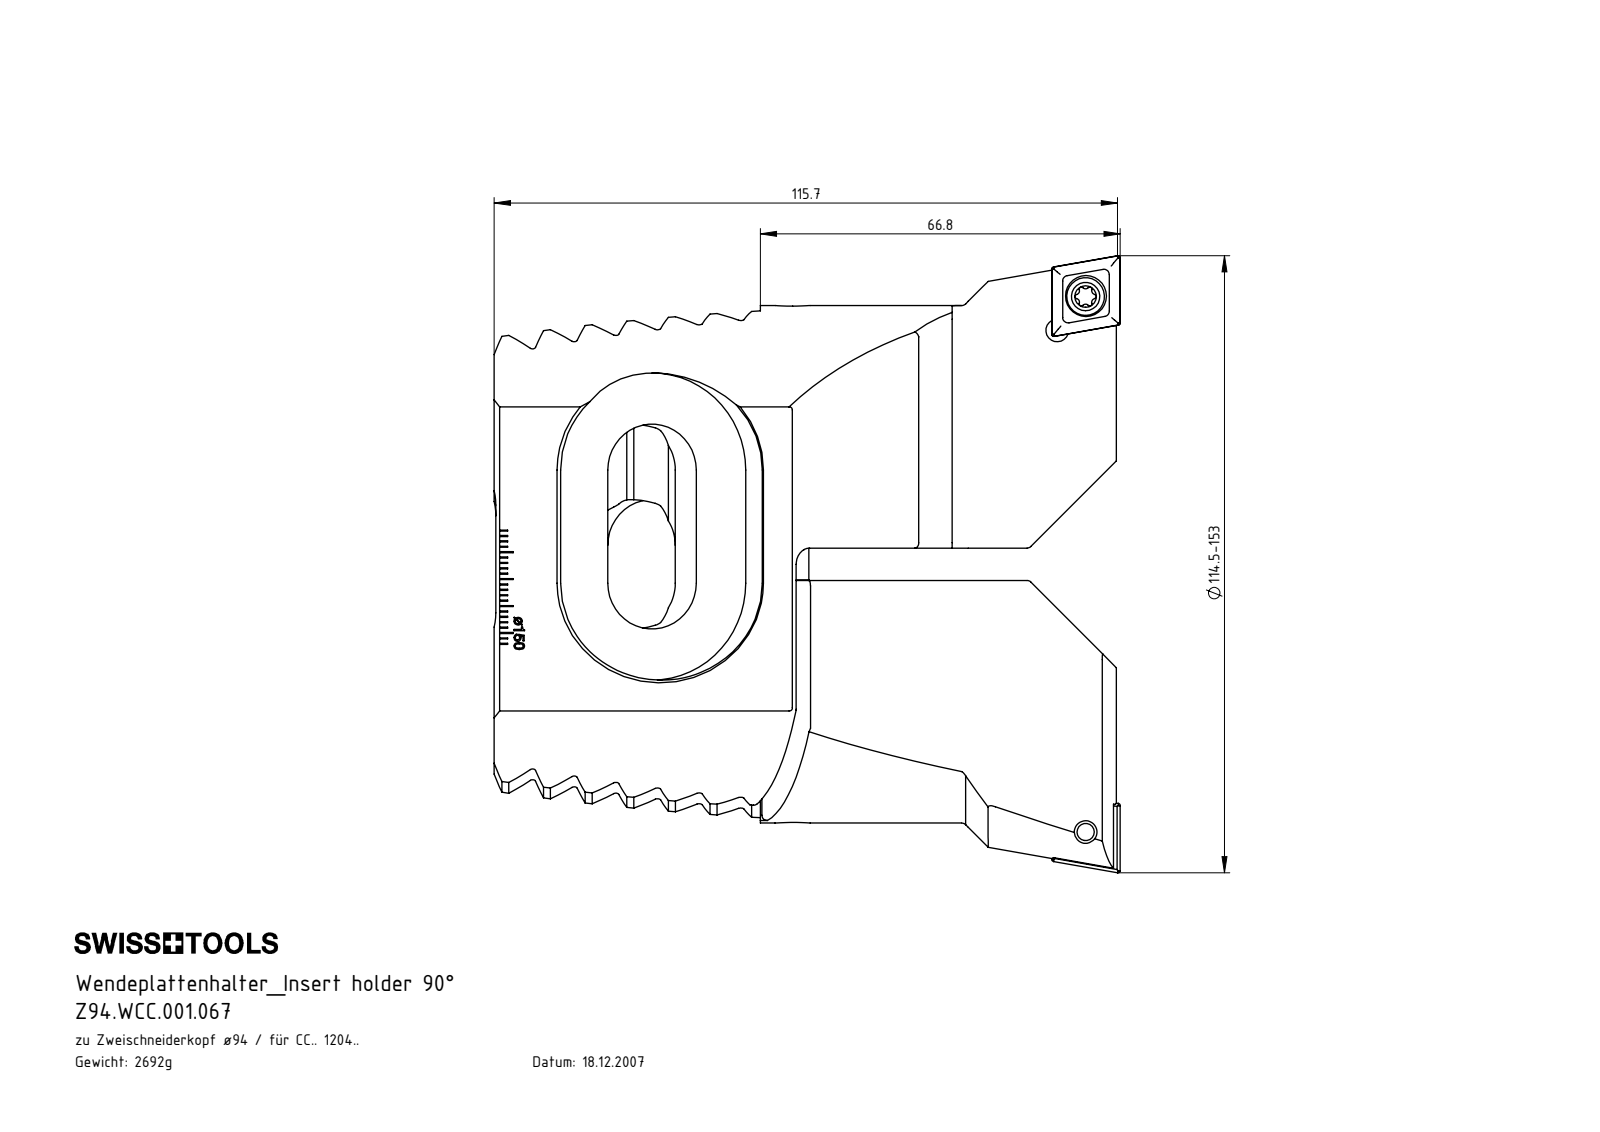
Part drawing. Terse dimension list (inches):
name: CCMT120404; Z94.WCC.001.067; WCC-ER2.001.010_A; Z94-xxx.001.067_E (+1 more)
written by: SolidWorks 2017 (AUTOMOTIVE_DESIGN)
unit: in
bodies: 8 solids, 782 faces (444 planar, 134 cylindrical, 204 other)
size: 4.575 × 4.508 × 2.961
volume: 20.93 in³; area: 99.83 in²
holes: 4× ⌀0.165, 2× ⌀0.079, 2× ⌀0.217, 2× ⌀0.299, 1× ⌀0.197
bosses: 2× ⌀0.276, 2× ⌀0.197, 1× ⌀0.236, 1× ⌀0.157
rounds: 16× R0.039, 12× R0.015, 12× R0.023, 12× R0.027, 6× R0.118, 4× R0.335, 4× R0.472, 4× R0.709
face distances: 0.273, 0.818, 1.091, 0.545, 0.546, 0.519, 1.469, 1.492, 0.272, 0.063
hole spacings: 0.323, 0.328, 0.984, 3.669, 3.673, 3.915, 1.902, 3.416
